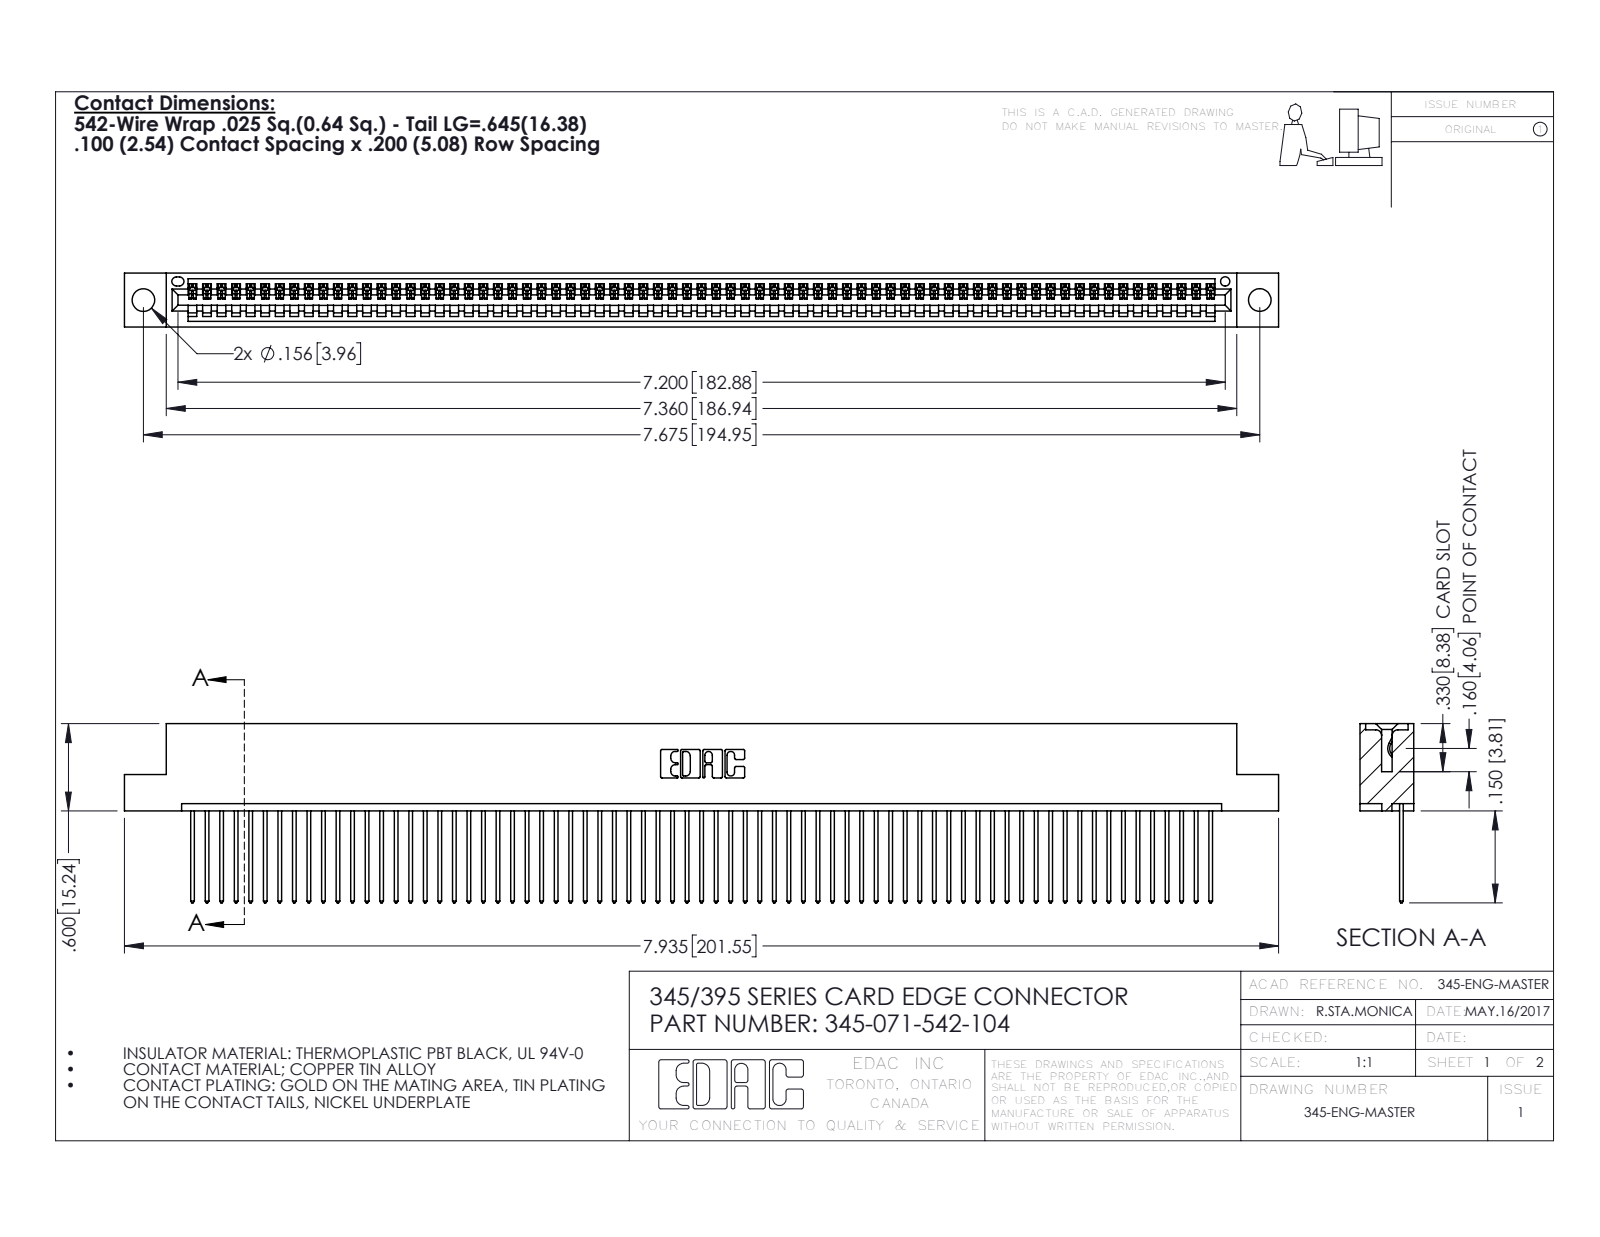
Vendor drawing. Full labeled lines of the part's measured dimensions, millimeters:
Part name (STEP PRODUCT): 345-292-001_345-293-142; 345 Part_Flush Mounting Lugs - 0.156 Dia-TH; 345-071-542-104
STEP written by: SolidWorks 2016 (CONFIG_CONTROL_DESIGN)
Units: millimetres
Bodies: 72 solids, 4244 faces (2920 planar, 1324 cylindrical, 0 other)
Overall size (bounding box): 201.5 × 31.3 × 9.4
Volume: 19 450 mm³ · Surface area: 27 050 mm²
Round holes (diameter × count): ⌀4 ×2, ⌀1.6 ×1
Partial cylindrical surfaces — rounded edges, fillets, slot ends (radius × count): R0.2 ×142, R0.3 ×142, R0.3 ×22, R0.2 ×6, R0.8 ×6, R0.7 ×3, R0.8 ×2, R1 ×2
Main face-to-face distances: 1.8, 7.6, 2.5, 6.9, 0.6, 9.4, 5.1, 5.7, 3.8, 1.8
Hole centre spacings: 6.9, 189, 194.9
